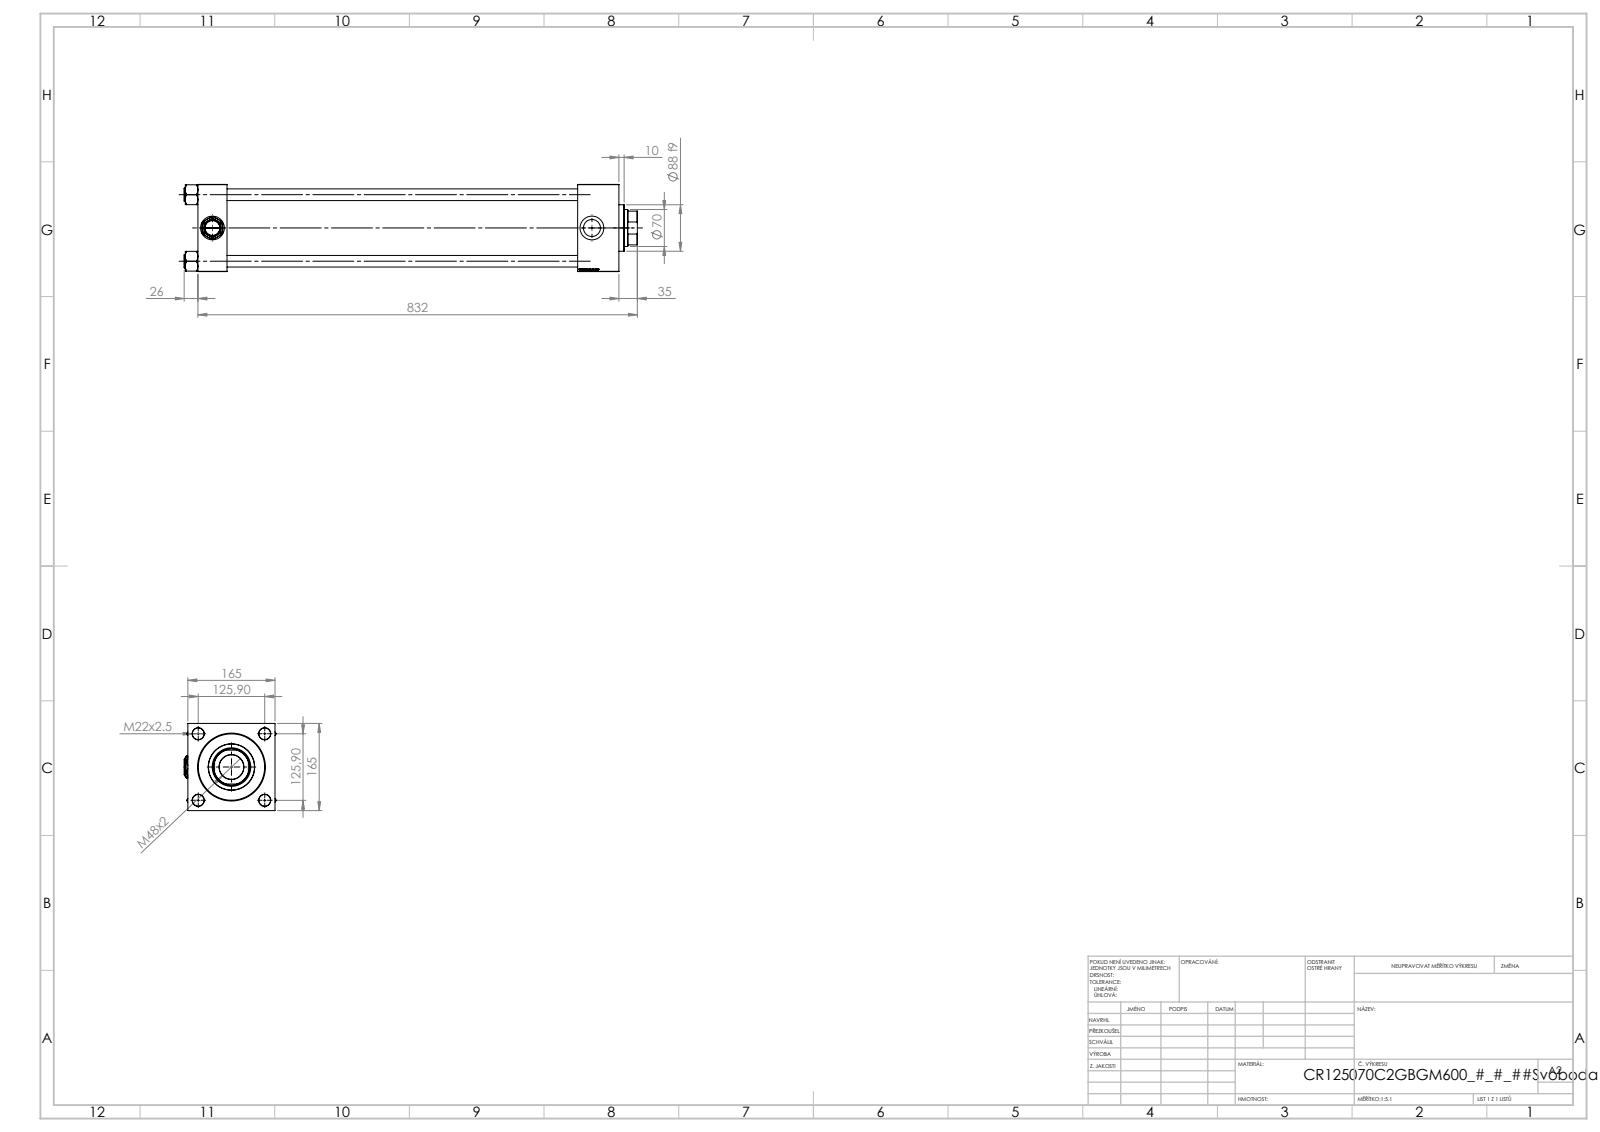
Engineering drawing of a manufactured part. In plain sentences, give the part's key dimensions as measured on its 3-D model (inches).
The part is named "NUT_M5_C; V215CR_VCP_C; V215_VC_A; Zatka_pro_OIL_PORT (+2 more)". Its 3-D file was written by "SolidWorks 2019 (CONFIG_CONTROL_DESIGN)". It is 12 solids with 1250 faces: 598 planar, 94 cylindrical and 558 other. Overall it measures 33.78 by 6.853 by 6.496 inches. Its volume is 513.4 cubic inches and its surface area 1 970 square inches. Round holes: 4 of diameter 0.866, 2 of diameter 0.276, 2 of diameter 1.269, 2 of diameter 1.772, 1 of diameter 1.831, 1 of diameter 2.756, 1 of diameter 2.874, 1 of diameter 3.78, 1 of diameter 4.921, 1 of diameter 4.941. Round bosses or shafts: 4 of diameter 0.984, 1 of diameter 5.157, 1 of diameter 3.465. Partial cylindrical surfaces (rounded edges, fillets, slot ends): 1 of radius 1.339. The main face-to-face distances are 6.496, 2.165, 31.378, 29.213, 3.071, 28.307, 26.142, 30.248, 28.083, 1.941. The hole center spacings are 3.505, 4.957, 7.01, 28.287.
